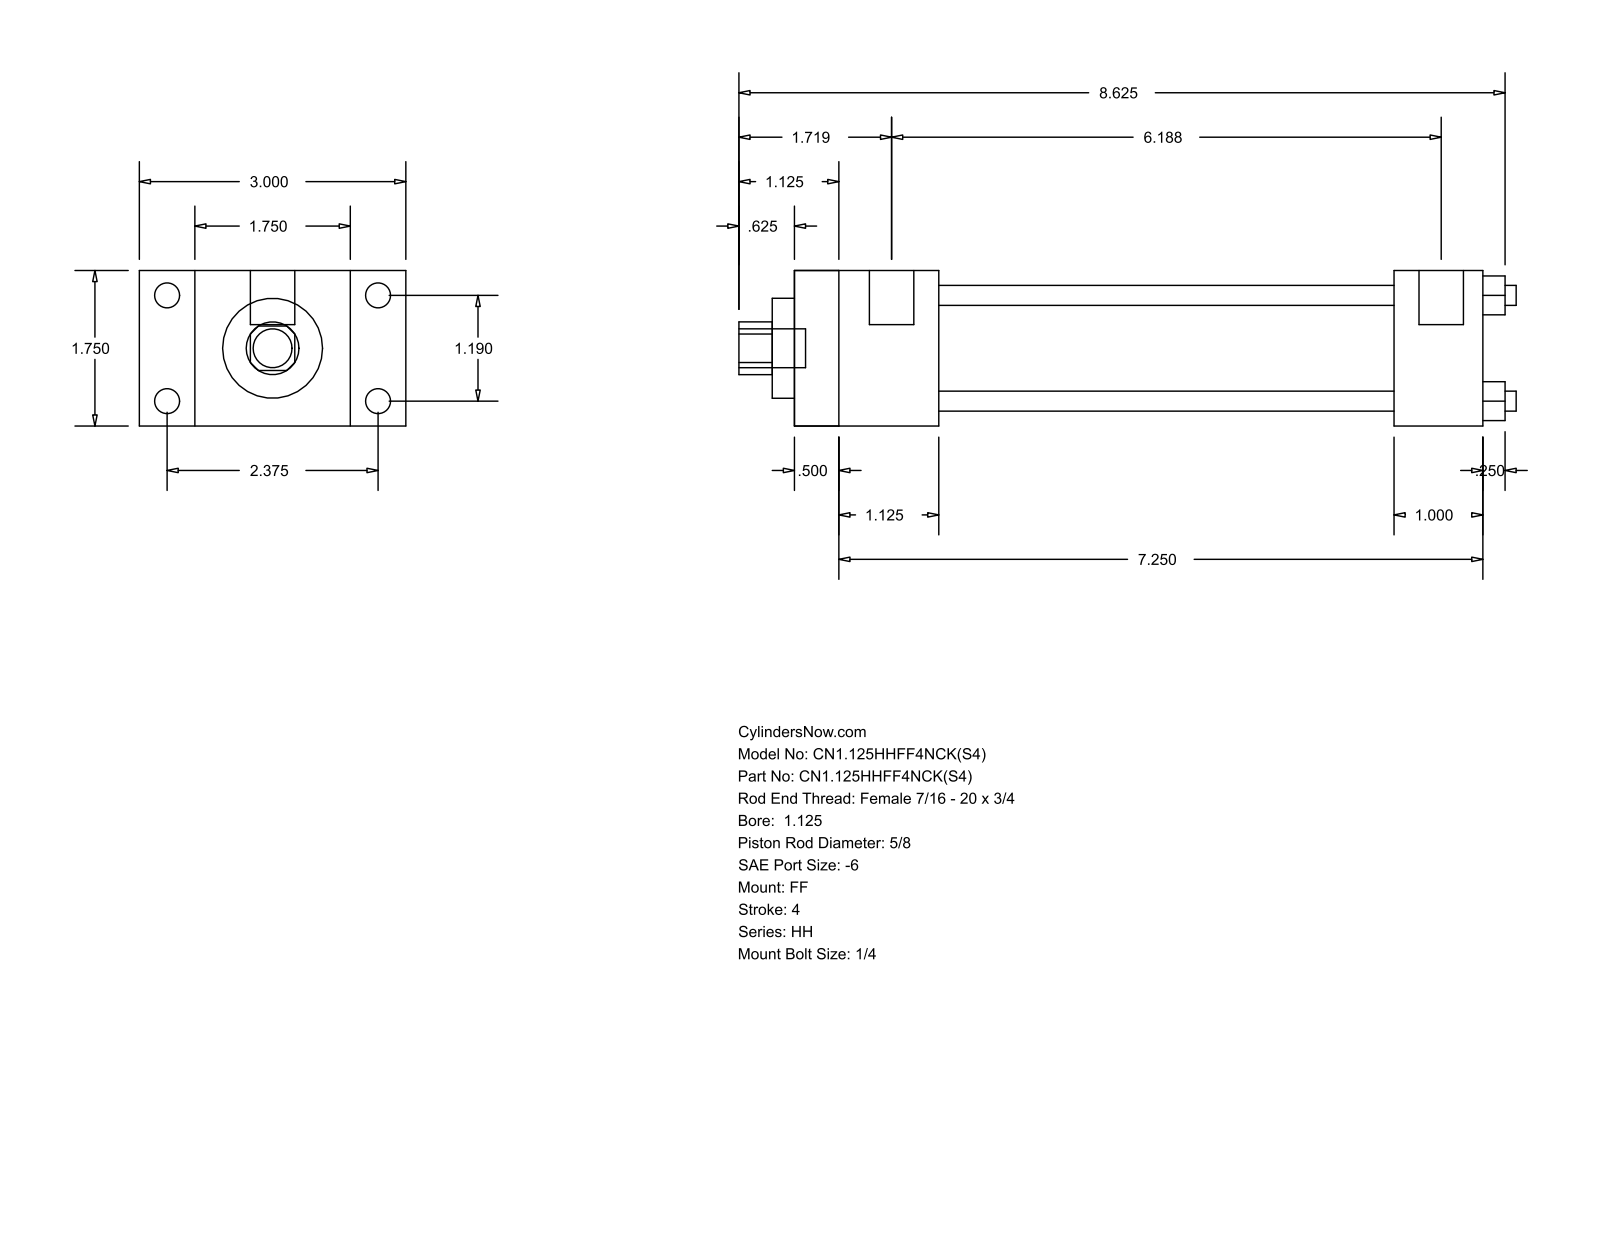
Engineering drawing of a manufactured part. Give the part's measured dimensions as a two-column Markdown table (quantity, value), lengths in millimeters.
| quantity | value |
| --- | --- |
| part name | HH_FF__0112_0.625 |
| STEP written by | GSSL Pune (CONFIG_CONTROL_DESIGN) |
| units | millimeters |
| bodies | 0 solids, 92 faces (64 planar, 28 cylindrical, 0 other) |
| overall size | 222.25 × 76.2 × 44.45 |
| round holes (diameter × count) | 5.71 × 4, 15.88 × 1, 28.57 × 1, 34.92 × 1 |
| round bosses / shafts (diameter × count) | 7.14 × 4, 5.56 × 4, 12.7 × 2, 11.11 × 1 |
| partial cylindrical surfaces (radius × count) | 7.54 × 1 |
| main face-to-face distances | 44.46, 196.84, 15.87, 12.69, 184.15, 60.33, 28.58, 41.27, 171.44, 158.75 |
| hole center spacings | 21.37, 30.22, 42.74 |
